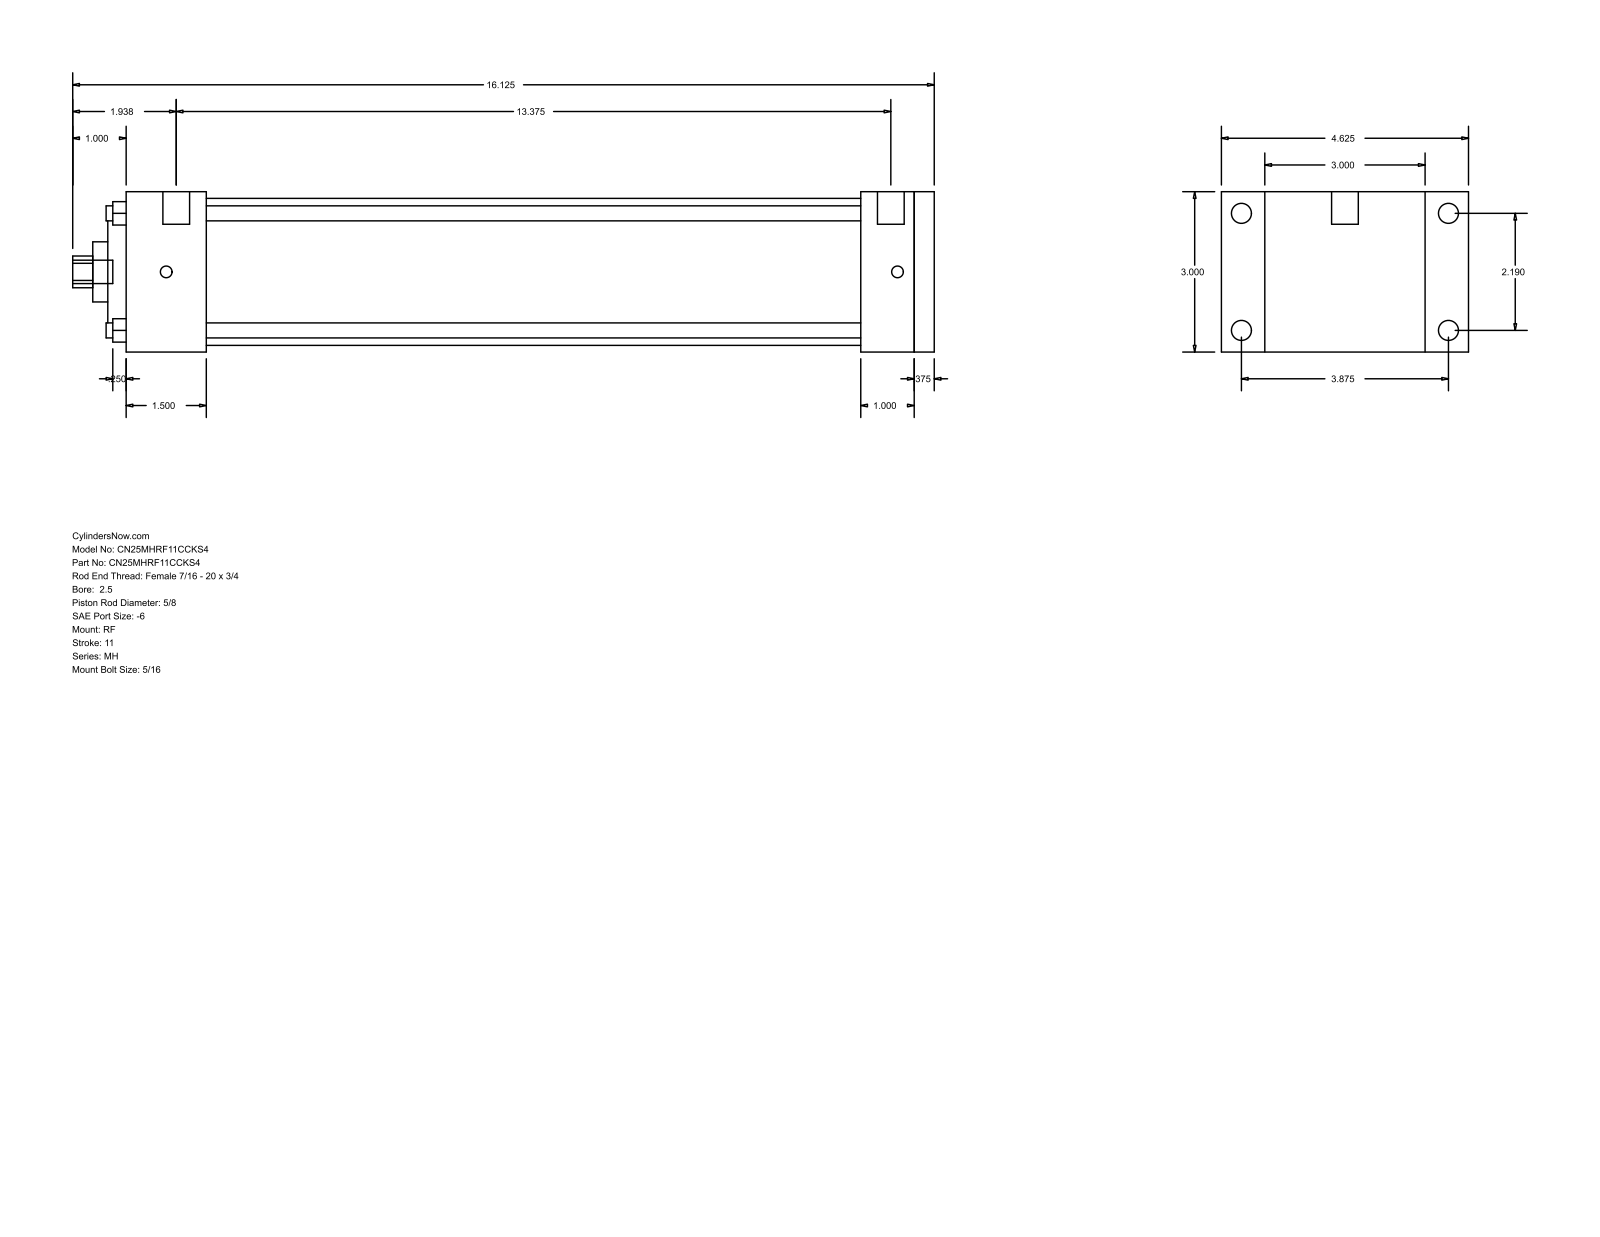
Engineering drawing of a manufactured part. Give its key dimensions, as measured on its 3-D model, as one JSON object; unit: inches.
{"part_name": "MH_RF__0250_0.625", "step_written_by": "GSSL Pune (CONFIG_CONTROL_DESIGN)", "units": "inches", "bodies": {"solids": 0, "faces": 94, "planar": 65, "cylindrical": 29, "other": 0}, "overall_size": [16.125, 4.625, 3], "round_holes": [[0.281, 4], [0.625, 1], [1.125, 1], [2.187, 1], [2.75, 1]], "round_bosses_or_shafts": [[0.375, 4], [0.219, 4], [0.5, 2], [0.437, 1]], "partial_cylinders_radius": [[0.297, 1]], "face_to_face_distances": [3, 0.375, 15.125, 14.75, 1, 13.75, 1.375, 1.5, 12.25, 13.25], "hole_center_spacings": [1.548, 2.19, 3.097]}
